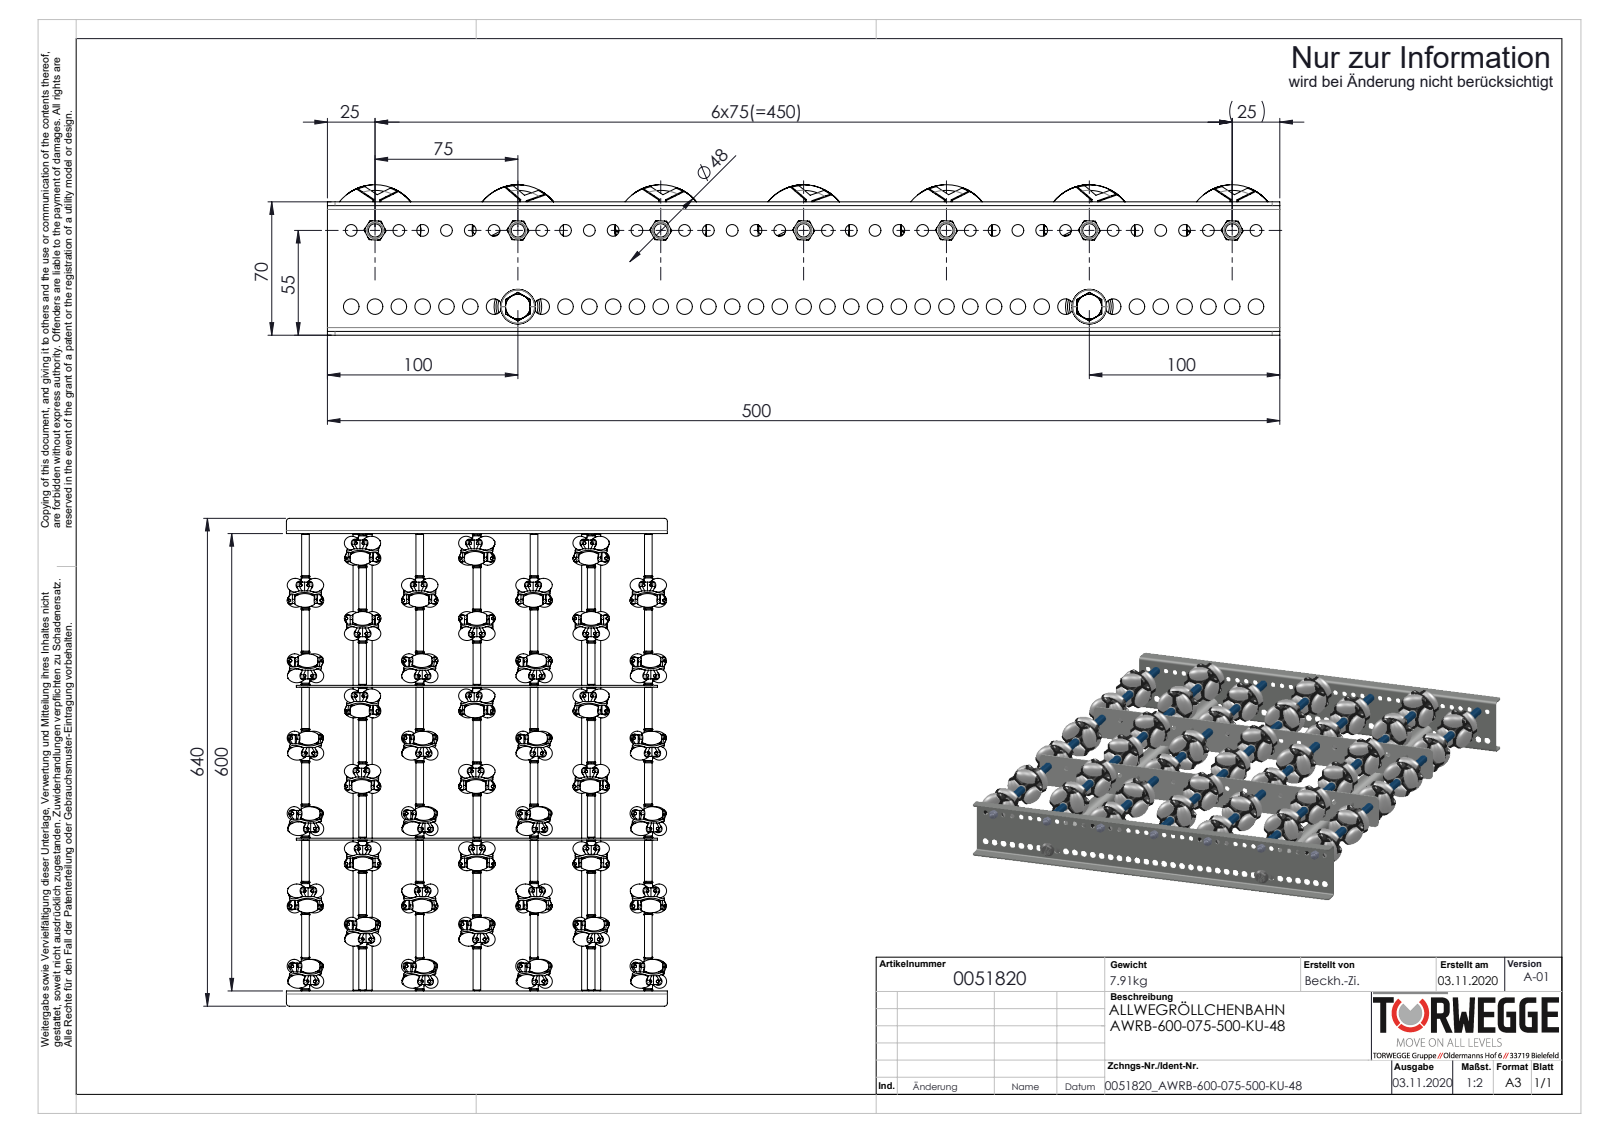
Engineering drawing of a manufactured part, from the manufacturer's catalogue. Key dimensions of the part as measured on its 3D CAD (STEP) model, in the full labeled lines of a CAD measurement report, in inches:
Part name (STEP PRODUCT): S100994_Sperrzahnschraube_M08x16-8.8-A2K; 0019719_Gewindestange-M6_L=620; S108767_Längstraverse-42x2,5-AWR_L500; AWR48_Halter (+8 more)
STEP written by: SolidWorks 2020 (AUTOMOTIVE_DESIGN)
Units: inches
Bodies: 707 solids, 12574 faces (4374 planar, 4890 cylindrical, 3310 other)
Overall size (bounding box): 25.197 × 19.685 × 3.11
Volume: 152.9 in³ · Surface area: 2 702 in²
Round holes (diameter × count): ⌀0.146 ×252, ⌀0.165 ×252, ⌀0.244 ×39, ⌀0.323 ×39, ⌀0.256 ×19, ⌀0.194 ×7, ⌀0.331 ×7, ⌀0.268 ×2, ⌀0.827 ×2
Round bosses / shafts (diameter × count): ⌀0.157 ×252, ⌀0.146 ×207, ⌀0.315 ×9, ⌀1.854 ×7, ⌀1.654 ×7, ⌀0.433 ×7, ⌀0.394 ×7, ⌀0.276 ×7
Partial cylindrical surfaces — rounded edges, fillets, slot ends (radius × count): R0.157 ×8, R0.079 ×4, R0.197 ×4
Main face-to-face distances: 0.079, 23.701, 7.894, 0.098, 2.677, 23.622, 23.78, 0.118, 0.581, 0.463
Hole centre spacings: 1.42, 1.419, 1.419, 1.42, 0.492, 0.984, 1.476, 3.445
